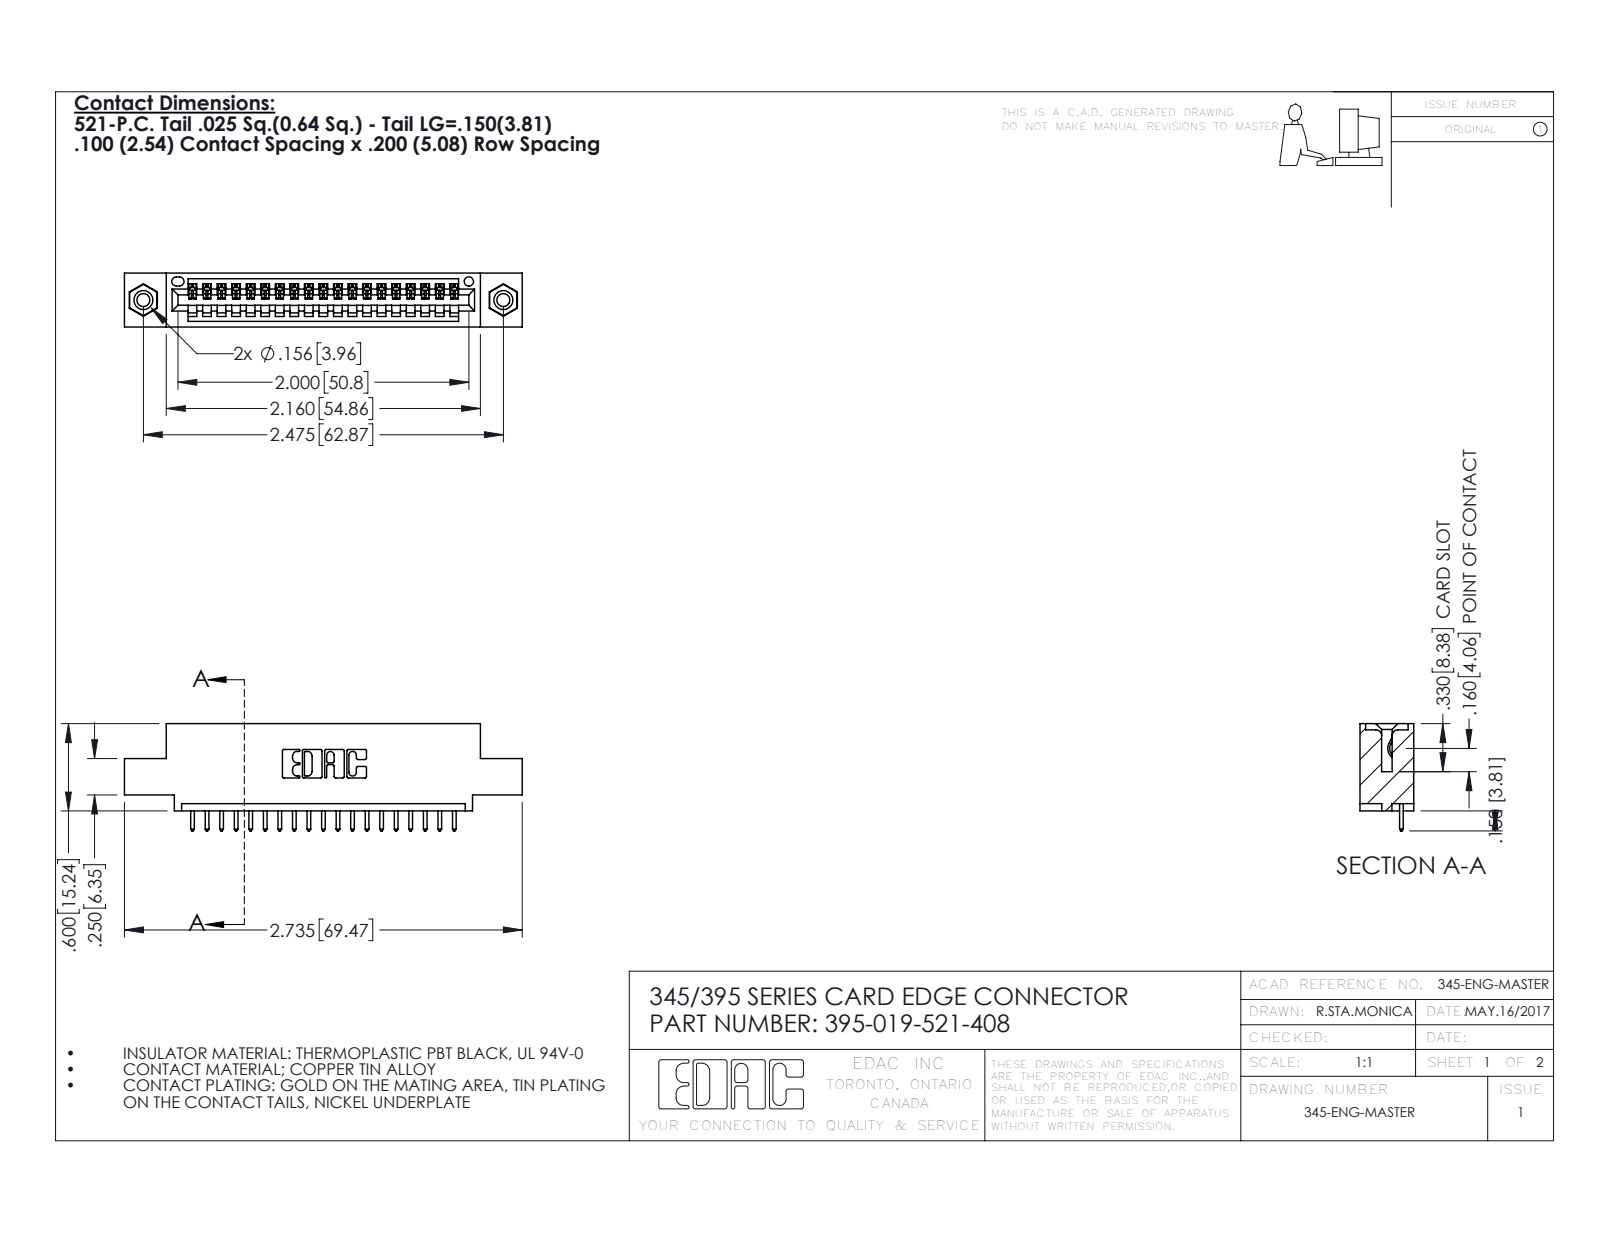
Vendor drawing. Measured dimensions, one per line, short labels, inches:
name: 345 Part_0.110 Offset - 0.156 Dia-TI; 395-019-521-408; 345-292-001_345-293-121; 345-250-001_345-250-003-102
written by: SolidWorks 2016 (CONFIG_CONTROL_DESIGN)
unit: in
bodies: 22 solids, 1292 faces (876 planar, 400 cylindrical, 16 other)
size: 2.735 × 0.737 × 0.37
volume: 0.383 in³; area: 12.27 in²
holes: 2× ⌀0.089, 2× ⌀0.125, 2× ⌀0.156, 1× ⌀0.064
bosses: 2× ⌀0.155
rounds: 38× R0.006, 38× R0.01, 22× R0.01, 6× R0.007, 6× R0.031, 3× R0.026, 2× R0.031, 2× R0.04
face distances: 0.072, 0.298, 0.2, 0.37, 0.098, 0.272, 0.025, 0.225, 0.149, 0.6
hole spacings: 0.27, 2.241, 2.475
